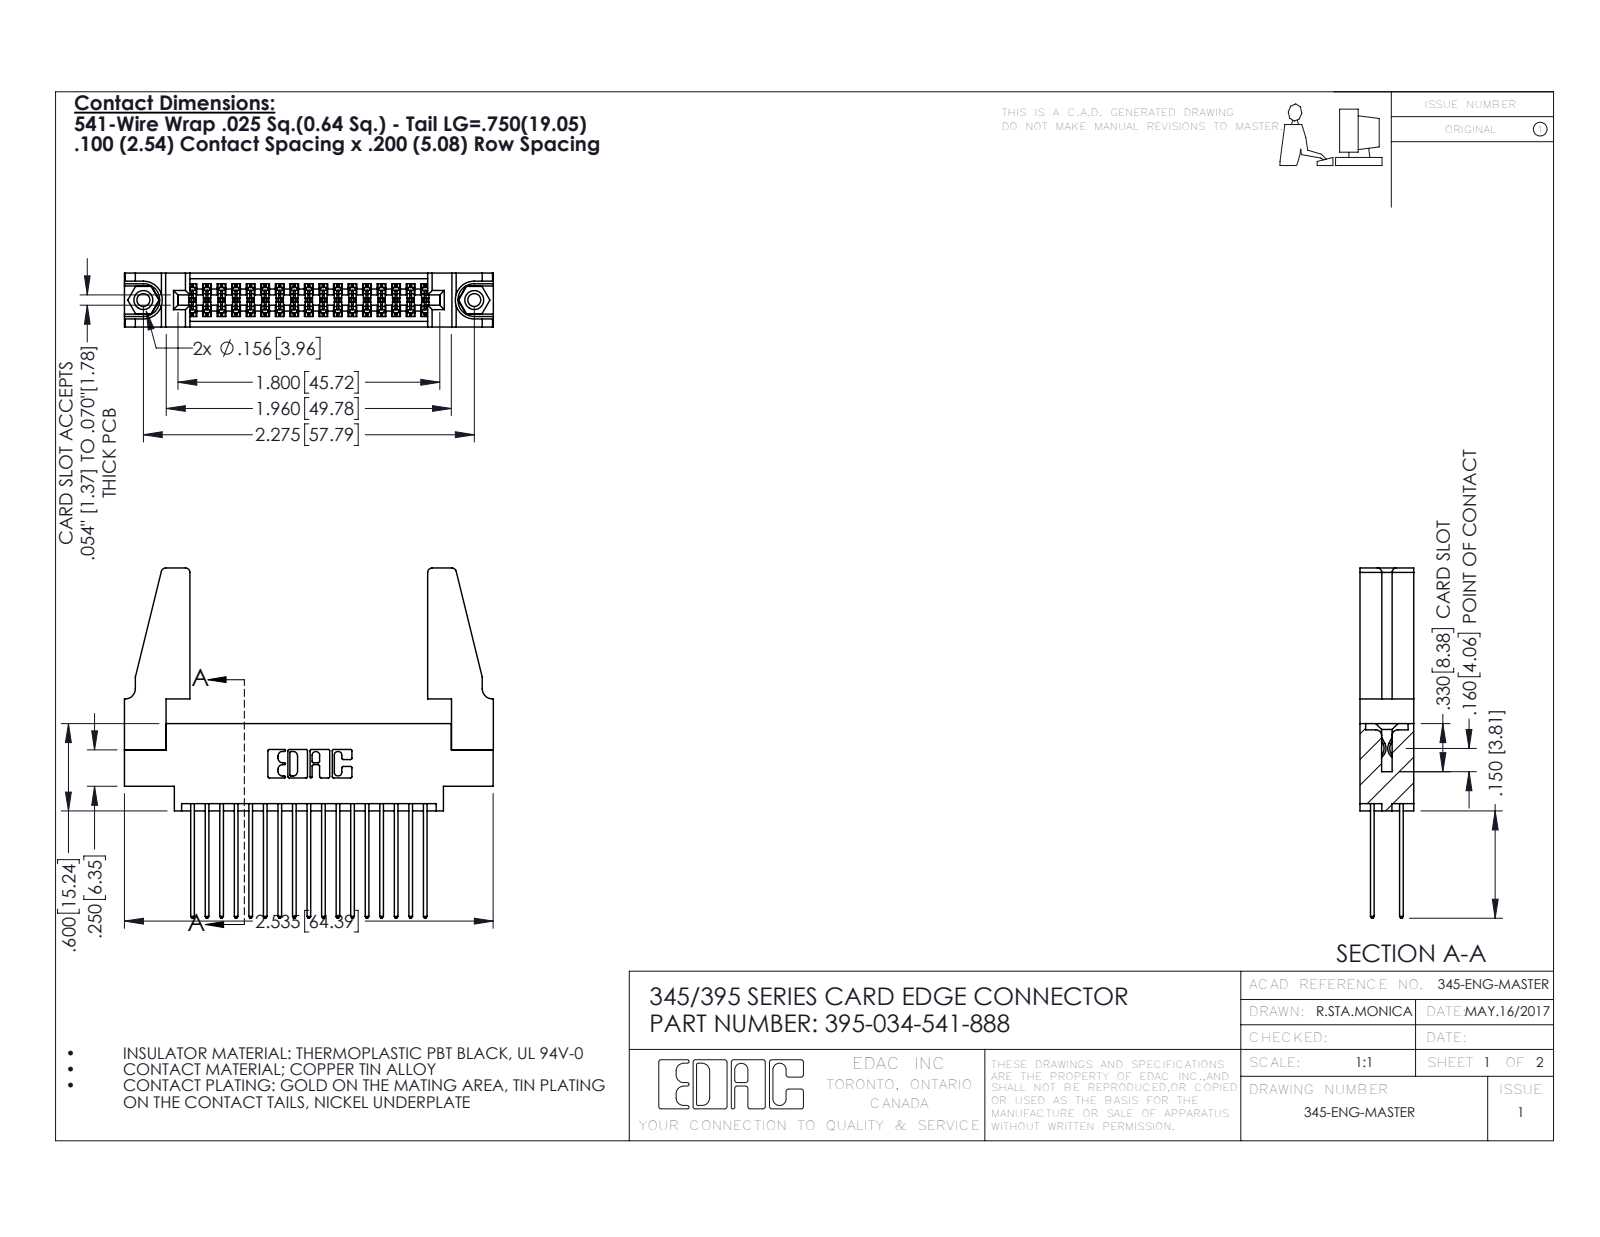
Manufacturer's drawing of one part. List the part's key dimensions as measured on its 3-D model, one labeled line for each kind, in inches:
Part name (STEP PRODUCT): 345-292-001_345-293-141; 345 Part_0.170 Offset - 0.156 Dia-TH; 345-250-001_345-250-001-102; 345-220-078_345-220-088 (+1 more)
STEP written by: SolidWorks 2016 (CONFIG_CONTROL_DESIGN)
Units: inches
Bodies: 39 solids, 1954 faces (1278 planar, 660 cylindrical, 16 other)
Overall size (bounding box): 2.536 × 2.407 × 0.37
Volume: 0.571 in³ · Surface area: 19.72 in²
Round holes (diameter × count): ⌀0.089 ×2, ⌀0.125 ×2, ⌀0.156 ×2, ⌀0.064 ×1
Round bosses / shafts (diameter × count): ⌀0.155 ×2
Partial cylindrical surfaces — rounded edges, fillets, slot ends (radius × count): R0.006 ×51, R0.01 ×34, R0.01 ×22, R0.03 ×8, R0.007 ×6, R0.031 ×6, R0.026 ×3, R0.014 ×2
Main face-to-face distances: 0.072, 0.298, 0.37, 0.2, 0.098, 0.272, 0.025, 0.225, 0.175, 0.15
Hole centre spacings: 0.27, 2.041, 2.275
